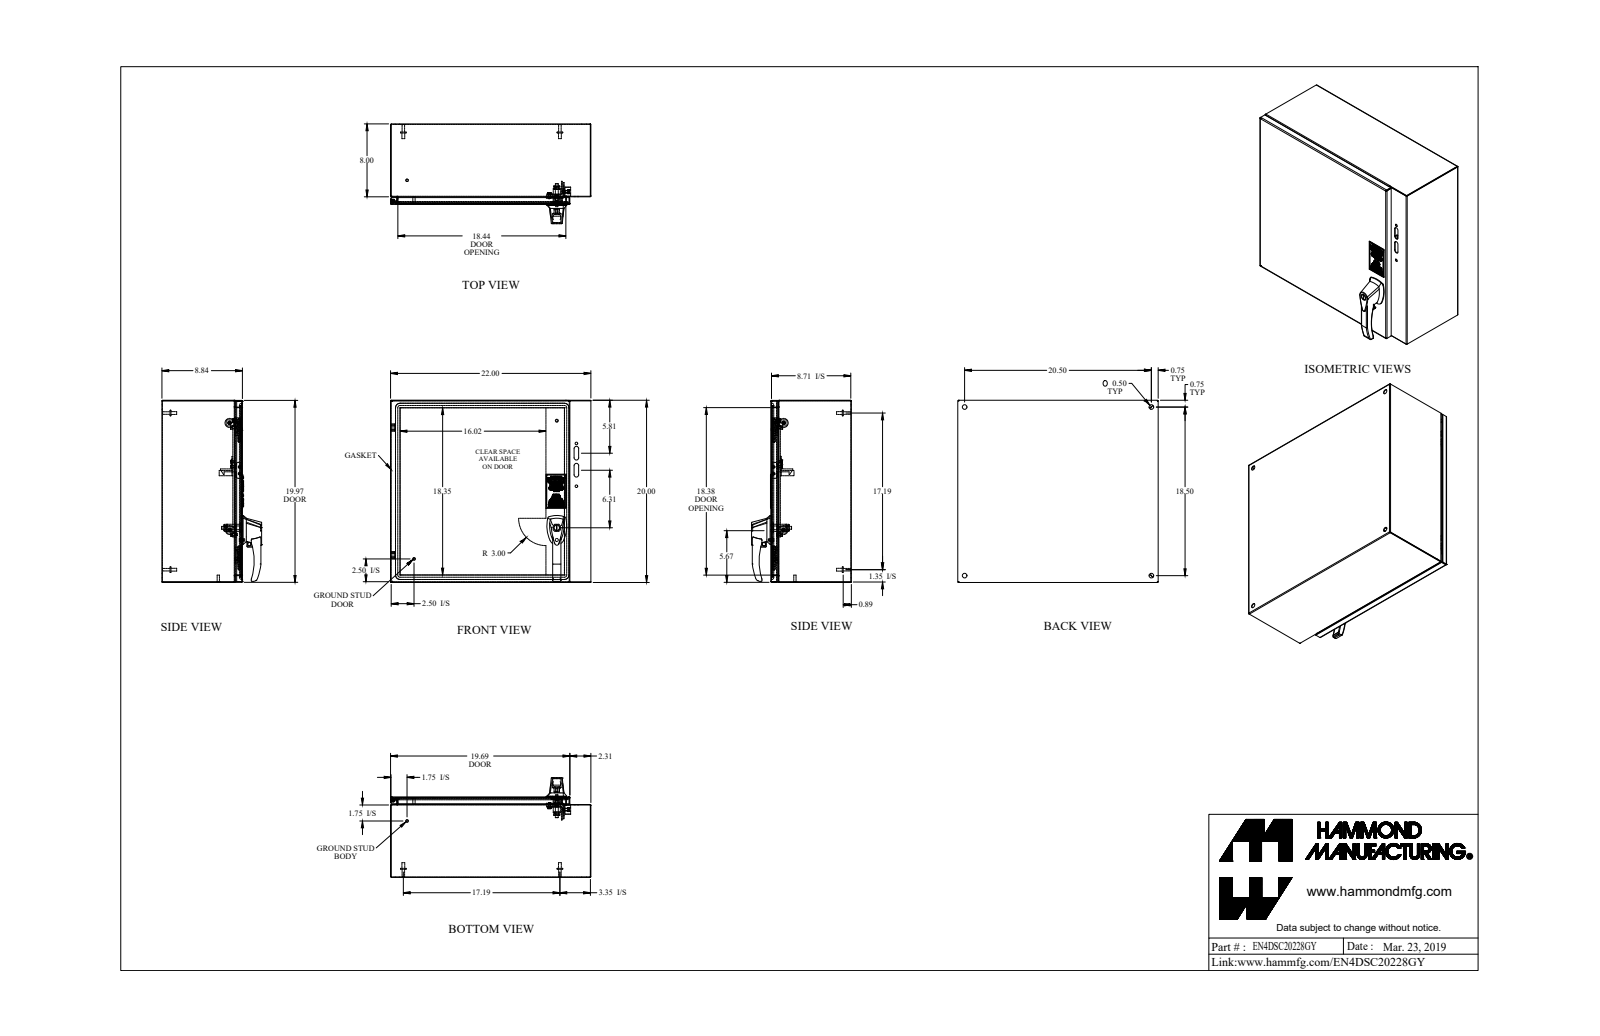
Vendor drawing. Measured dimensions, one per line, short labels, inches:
name: EN4DSC20228GY
written by: SolidWorks 2019 (AUTOMOTIVE_DESIGN)
unit: in
bodies: 45 solids, 929 faces (502 planar, 284 cylindrical, 143 other)
size: 21.997 × 20 × 10.952
volume: 145.2 in³; area: 3 714 in²
holes: 4× ⌀0.176, 2× ⌀0.156, 2× ⌀0.173, 2× ⌀0.215, 2× ⌀0.25, 2× ⌀0.265, 2× ⌀0.281, 2× ⌀0.413, 1× ⌀0.172, 1× ⌀0.196, 1× ⌀0.233, 1× ⌀0.24
bosses: 7× ⌀0.25, 4× ⌀0.375, 4× ⌀0.313, 4× ⌀0.27, 4× ⌀0.156, 2× ⌀1, 2× ⌀0.625, 2× ⌀0.625
rounds: 28× R0.079, 16× R0.007, 14× R0.25, 11× R0.125, 8× R0.151, 7× R0.06, 6× R0.03, 6× R0.09
face distances: 0.072, 8.765, 8.693, 8.837, 19.928, 21.916, 20, 19.856, 0.837, 7.928
hole spacings: 11.75, 1.11, 0.52, 0.75, 0.817, 0.992, 1.004, 1.139
